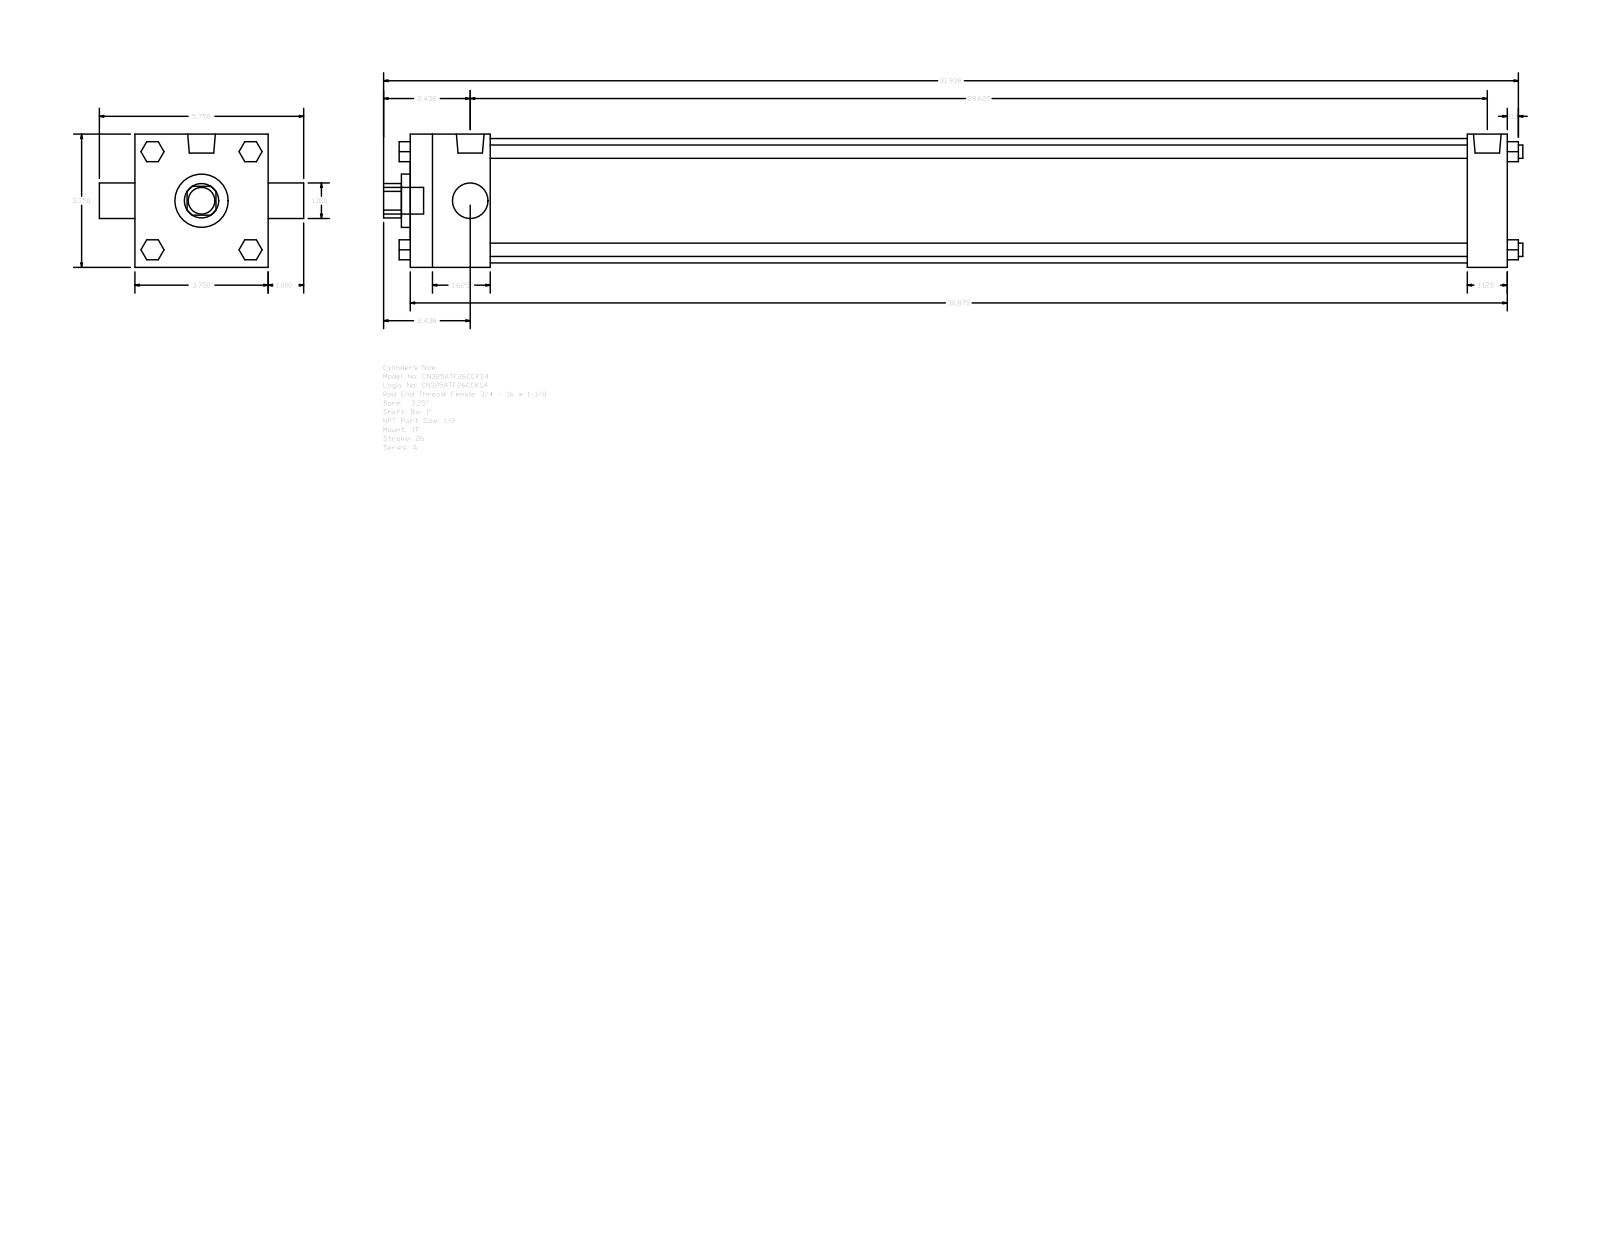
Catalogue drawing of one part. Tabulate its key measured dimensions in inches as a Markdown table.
| quantity | value |
| --- | --- |
| part name | A_TF__0325_1 |
| STEP written by | GSSL Pune (CONFIG_CONTROL_DESIGN) |
| units | inches |
| bodies | 0 solids, 120 faces (92 planar, 28 cylindrical, 0 other) |
| overall size | 32.063 × 5.75 × 3.75 |
| round holes (diameter × count) | 1 × 2, 1.5 × 1, 3.5 × 1 |
| round bosses / shafts (diameter × count) | 0.375 × 4, 0.344 × 3, 0.778 × 2, 0.75 × 1 |
| partial cylindrical surfaces (radius × count) | 0.484 × 1 |
| main face-to-face distances | 3.75, 30.875, 1.125, 2.25, 29.75, 27.5, 28.625, 0.562, 1.38, 2.39 |
